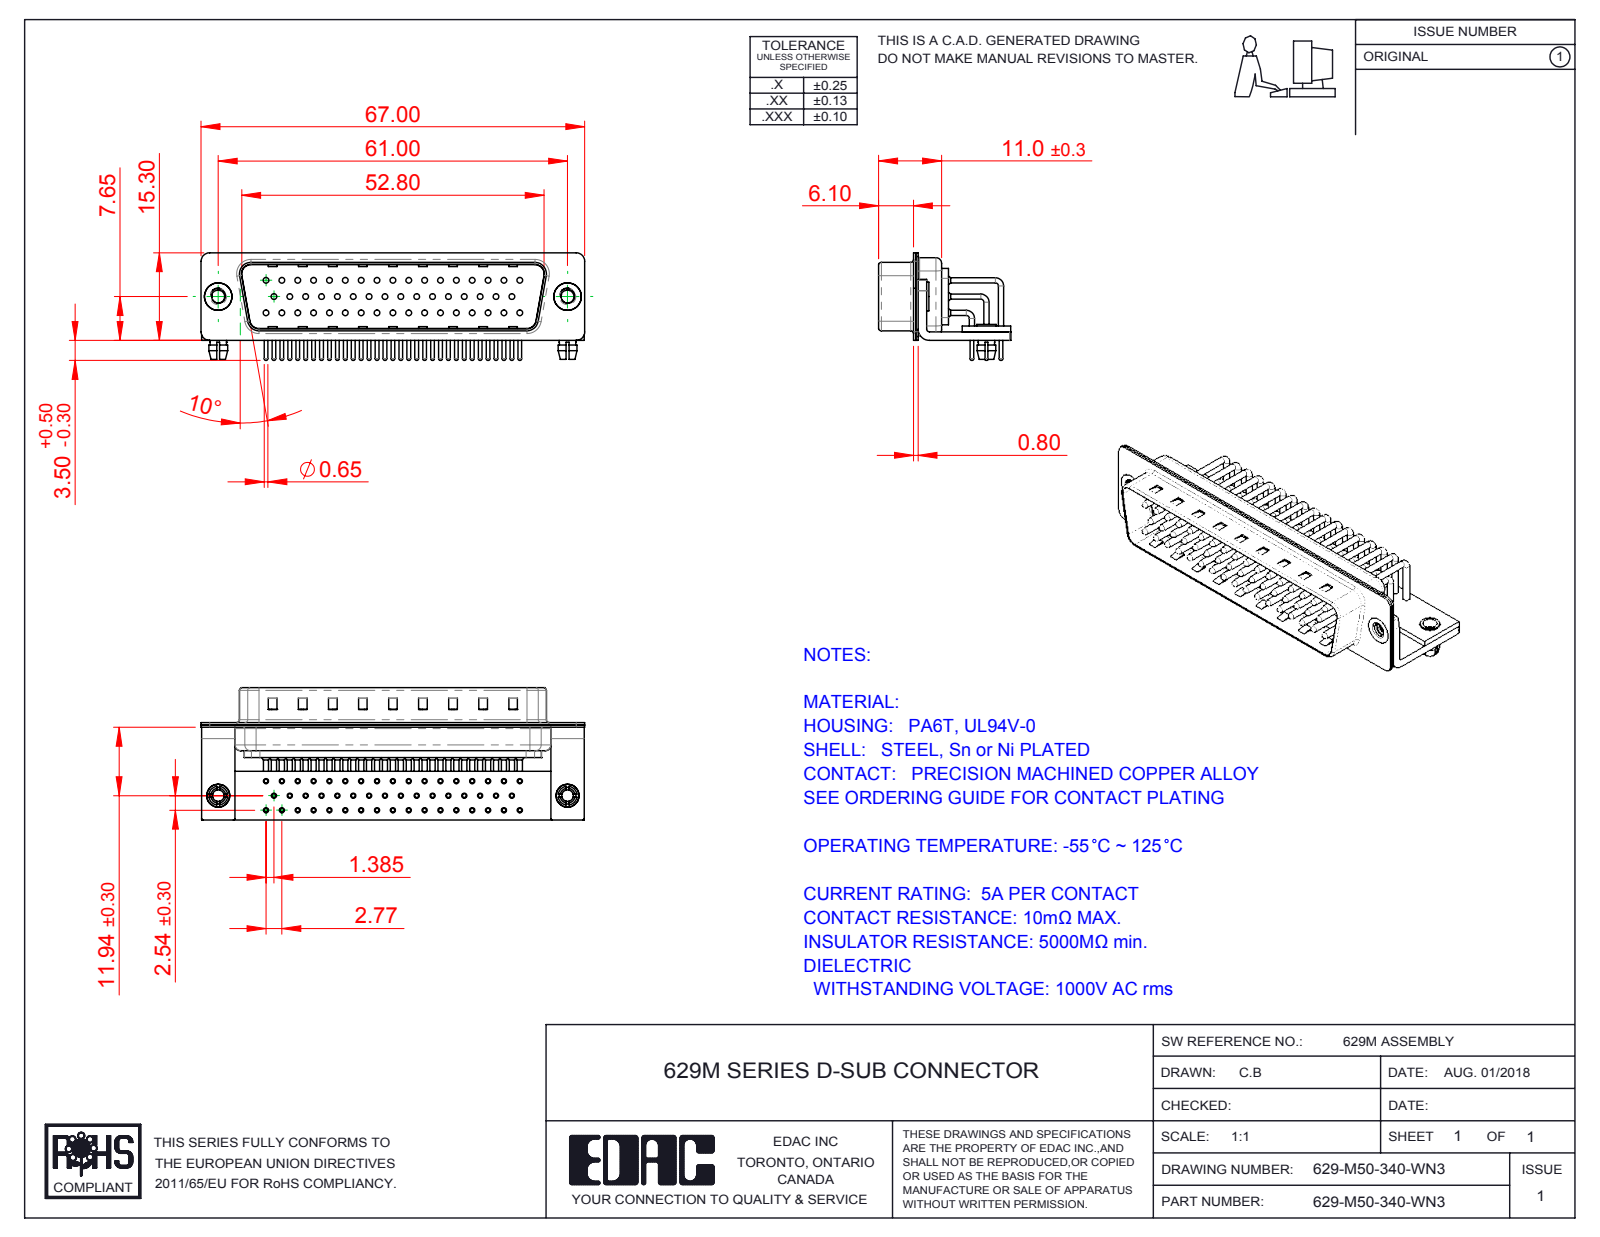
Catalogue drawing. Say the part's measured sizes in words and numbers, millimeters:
The part is named "629M Board Lock_50 Contacts; 629-M50-340-WN3; 629M Stabilizer Board_50 Contacts; 629M 4-40 Threaded Rivet_Stabilizer (+7 more)". Its 3-D file was written by "SolidWorks 2016 (CONFIG_CONTROL_DESIGN)". It is 60 solids with 6154 faces: 3477 planar, 2095 cylindrical and 582 other. Overall it measures 67 by 23.1 by 18.8 millimeters. Its volume is 5 879 cubic millimeters and its surface area 15 169 square millimeters. Round holes: 52 of diameter 2, 50 of diameter 0.9, 50 of diameter 1, 50 of diameter 1.7, 2 of diameter 2.26, 2 of diameter 2.5, 2 of diameter 3.2, 2 of diameter 4, 2 of diameter 4.8. Round bosses or shafts: 58 of diameter 0.9, 50 of diameter 1.5, 50 of diameter 0.65, 2 of diameter 5, 2 of diameter 4.9, 2 of diameter 4, 2 of diameter 3.4, 2 of diameter 3.3. Partial cylindrical surfaces (rounded edges, fillets, slot ends): 50 of radius 1.01, 16 of radius 0.25, 16 of radius 1.5, 13 of radius 2, 9 of radius 0.5, 8 of radius 1.6, 4 of radius 0.6, 4 of radius 0.65. The main face-to-face distances are 0.4, 1, 11.55, 1.5, 0.83, 5.7, 0.43, 11.95, 1.9, 0.8. The hole center spacings are 2.77, 5.54, 8.31, 11.08, 13.85, 16.62, 3.16, 19.39.
